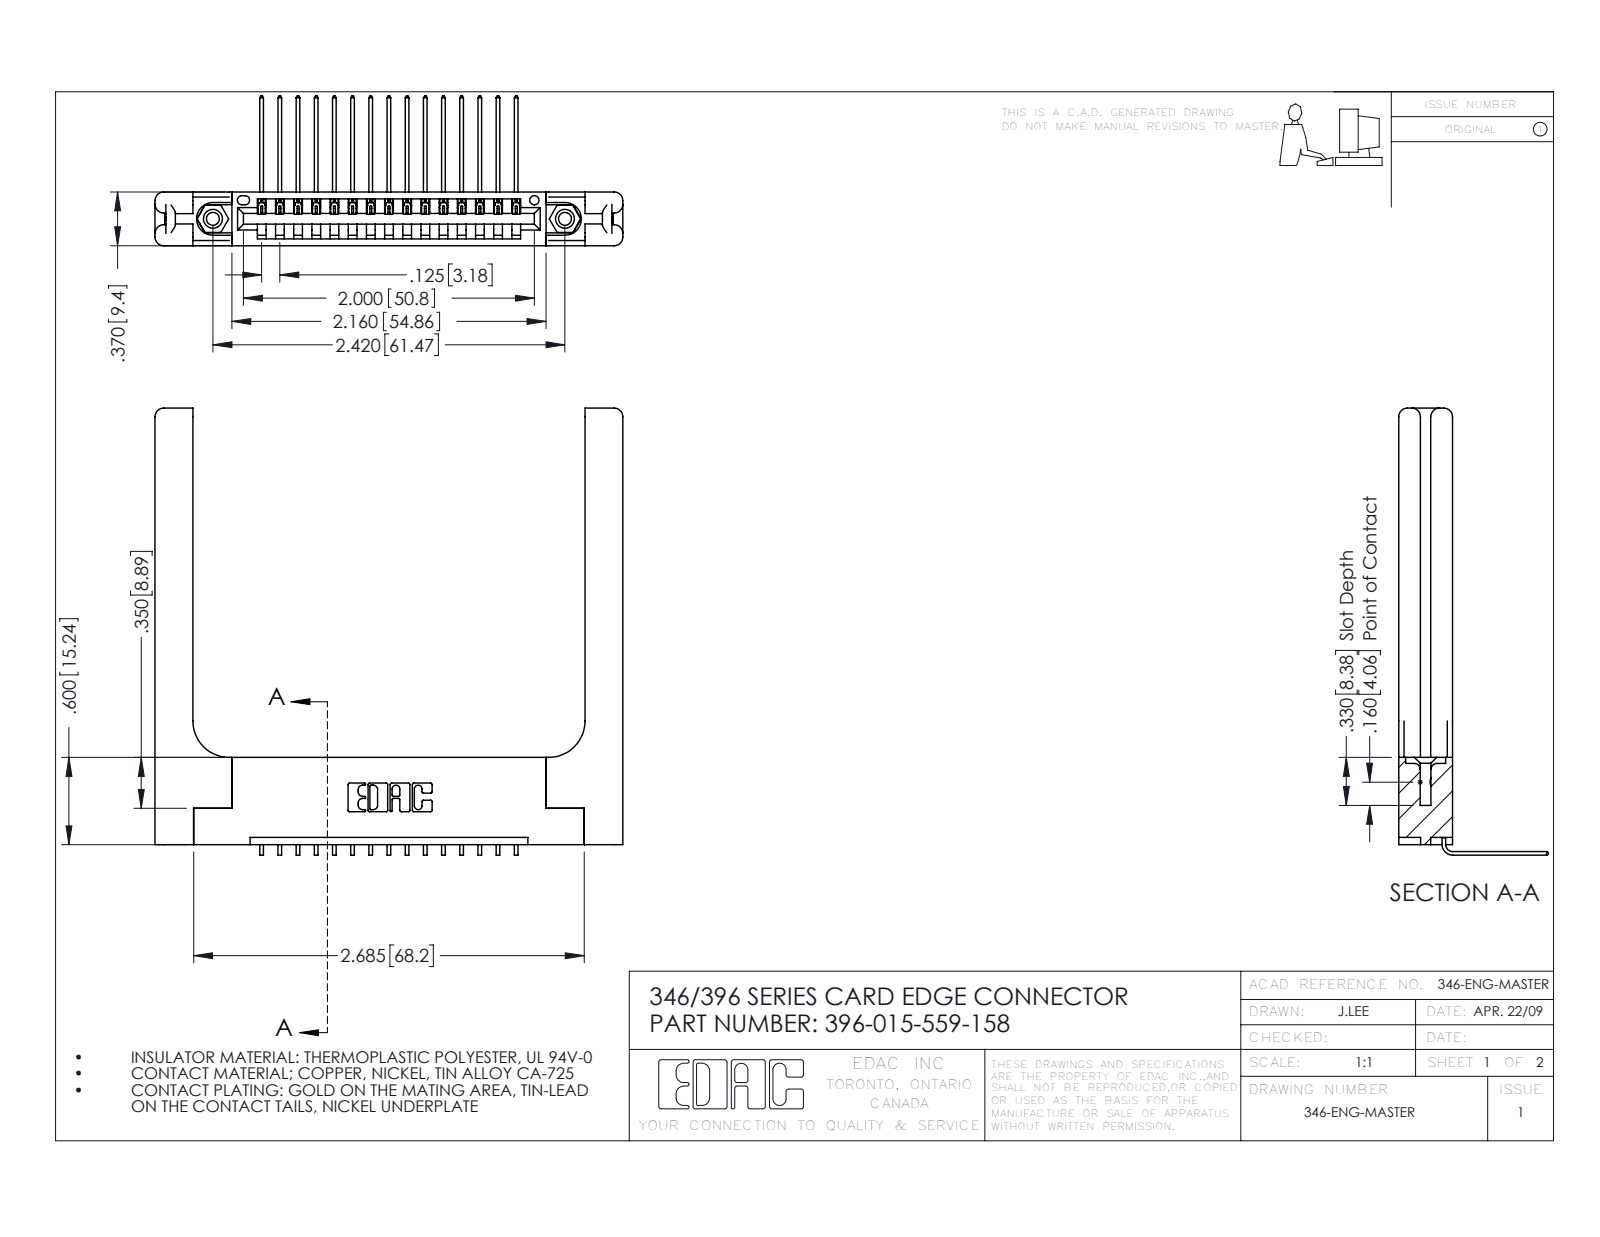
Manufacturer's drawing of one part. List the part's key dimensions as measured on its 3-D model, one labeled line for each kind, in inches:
Part name (STEP PRODUCT): 346-220-058_345-220-058; 345-250-001_345-250-001-102; 396-015-559-158; 345-292-001_558 559 Tail - 1 (+1 more)
STEP written by: SolidWorks 2016 (CONFIG_CONTROL_DESIGN)
Units: inches
Bodies: 20 solids, 1278 faces (854 planar, 364 cylindrical, 60 other)
Overall size (bounding box): 3.216 × 3.073 × 1.03
Volume: 0.928 in³ · Surface area: 22.91 in²
Round holes (diameter × count): ⌀0.089 ×2, ⌀0.125 ×2, ⌀0.156 ×2, ⌀0.064 ×1
Round bosses / shafts (diameter × count): ⌀0.155 ×2
Partial cylindrical surfaces — rounded edges, fillets, slot ends (radius × count): R0.006 ×30, R0.01 ×22, R0.06 ×16, R0.007 ×6, R0.031 ×6, R0.026 ×3, R0.03 ×2, R0.031 ×2
Main face-to-face distances: 0.37, 0.15, 0.072, 0.322, 0.048, 0.148, 0.25, 0.22, 0.102, 0.173
Hole centre spacings: 0.246, 2.213, 2.42
